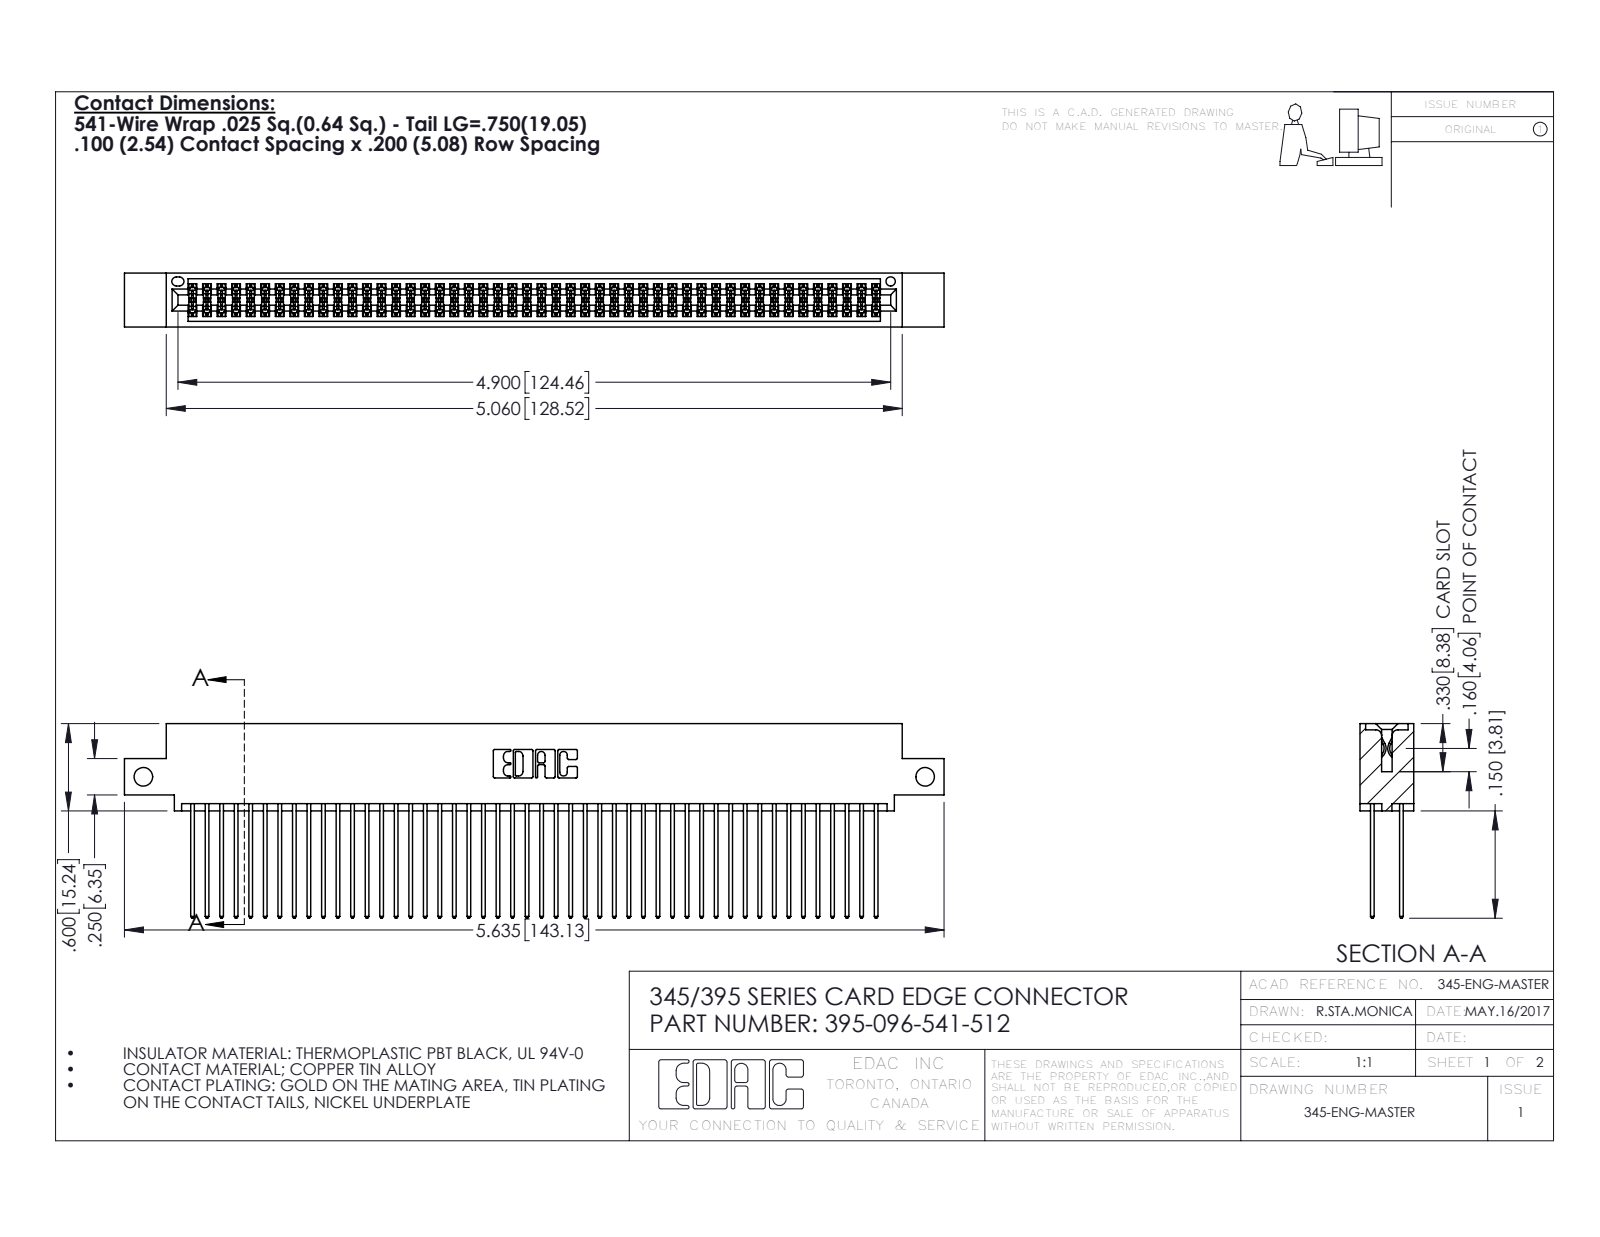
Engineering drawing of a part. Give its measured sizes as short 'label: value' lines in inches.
name: 395-096-541-512; 345 Part_0.110 Offset - Side Mount; 345-292-001_345-293-141
written by: SolidWorks 2016 (CONFIG_CONTROL_DESIGN)
unit: in
bodies: 97 solids, 4930 faces (3252 planar, 1678 cylindrical, 0 other)
size: 5.635 × 1.337 × 0.37
volume: 0.876 in³; area: 37 in²
holes: 2× ⌀0.128, 1× ⌀0.064
rounds: 144× R0.006, 96× R0.01, 22× R0.01, 6× R0.007, 6× R0.031, 3× R0.026, 2× R0.014, 2× R0.019
face distances: 0.298, 0.072, 0.2, 0.098, 0.272, 0.025, 0.225, 0.37, 0.175, 0.149
hole spacings: 5.375
